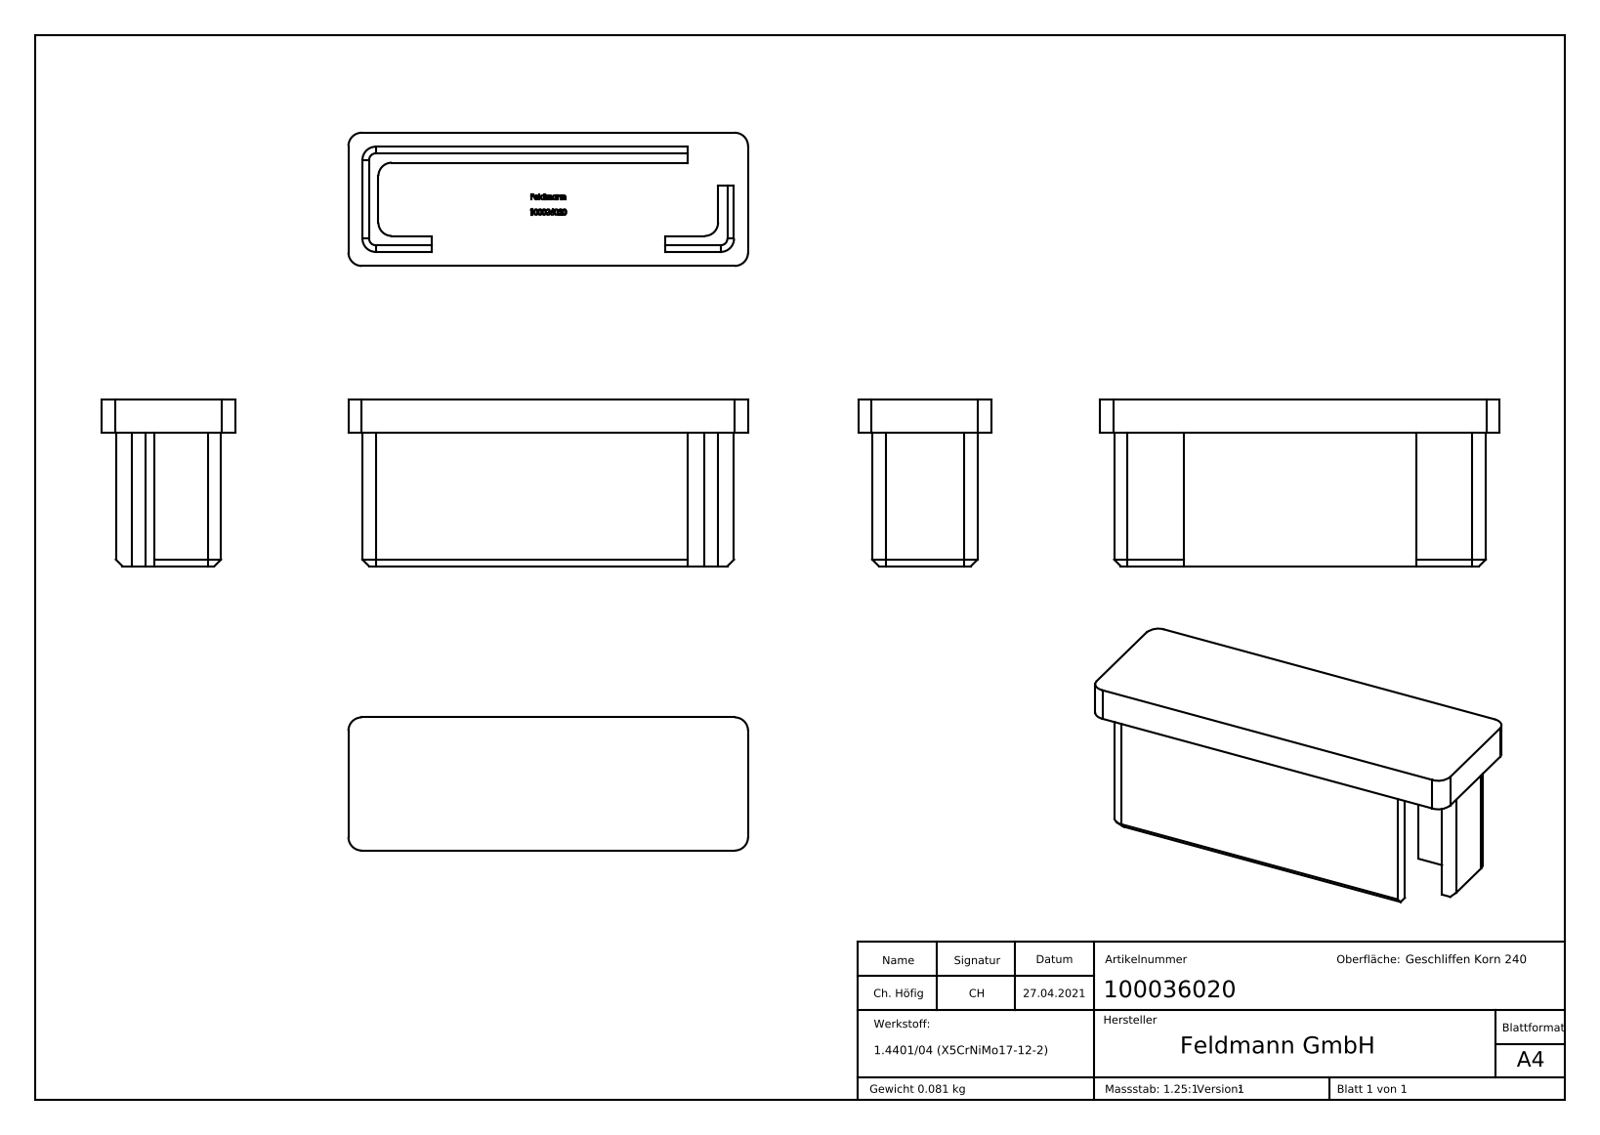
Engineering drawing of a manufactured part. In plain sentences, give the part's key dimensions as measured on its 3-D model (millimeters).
The part is named "100036020". Its 3-D file was written by "SolidWorks 2018 (CONFIG_CONTROL_DESIGN)". It is 1 solid with 260 faces: 125 planar, 10 cylindrical and 125 other. Overall it measures 60 by 25 by 20 millimeters. Its volume is 10 175 cubic millimeters and its surface area 6 746 square millimeters. Partial cylindrical surfaces (rounded edges, fillets, slot ends): 10 of radius 2. The main face-to-face distances are 2.4, 5, 4.5, 2.1, 17.9, 13.4, 15.5, 20, 15.8, 53.4.
